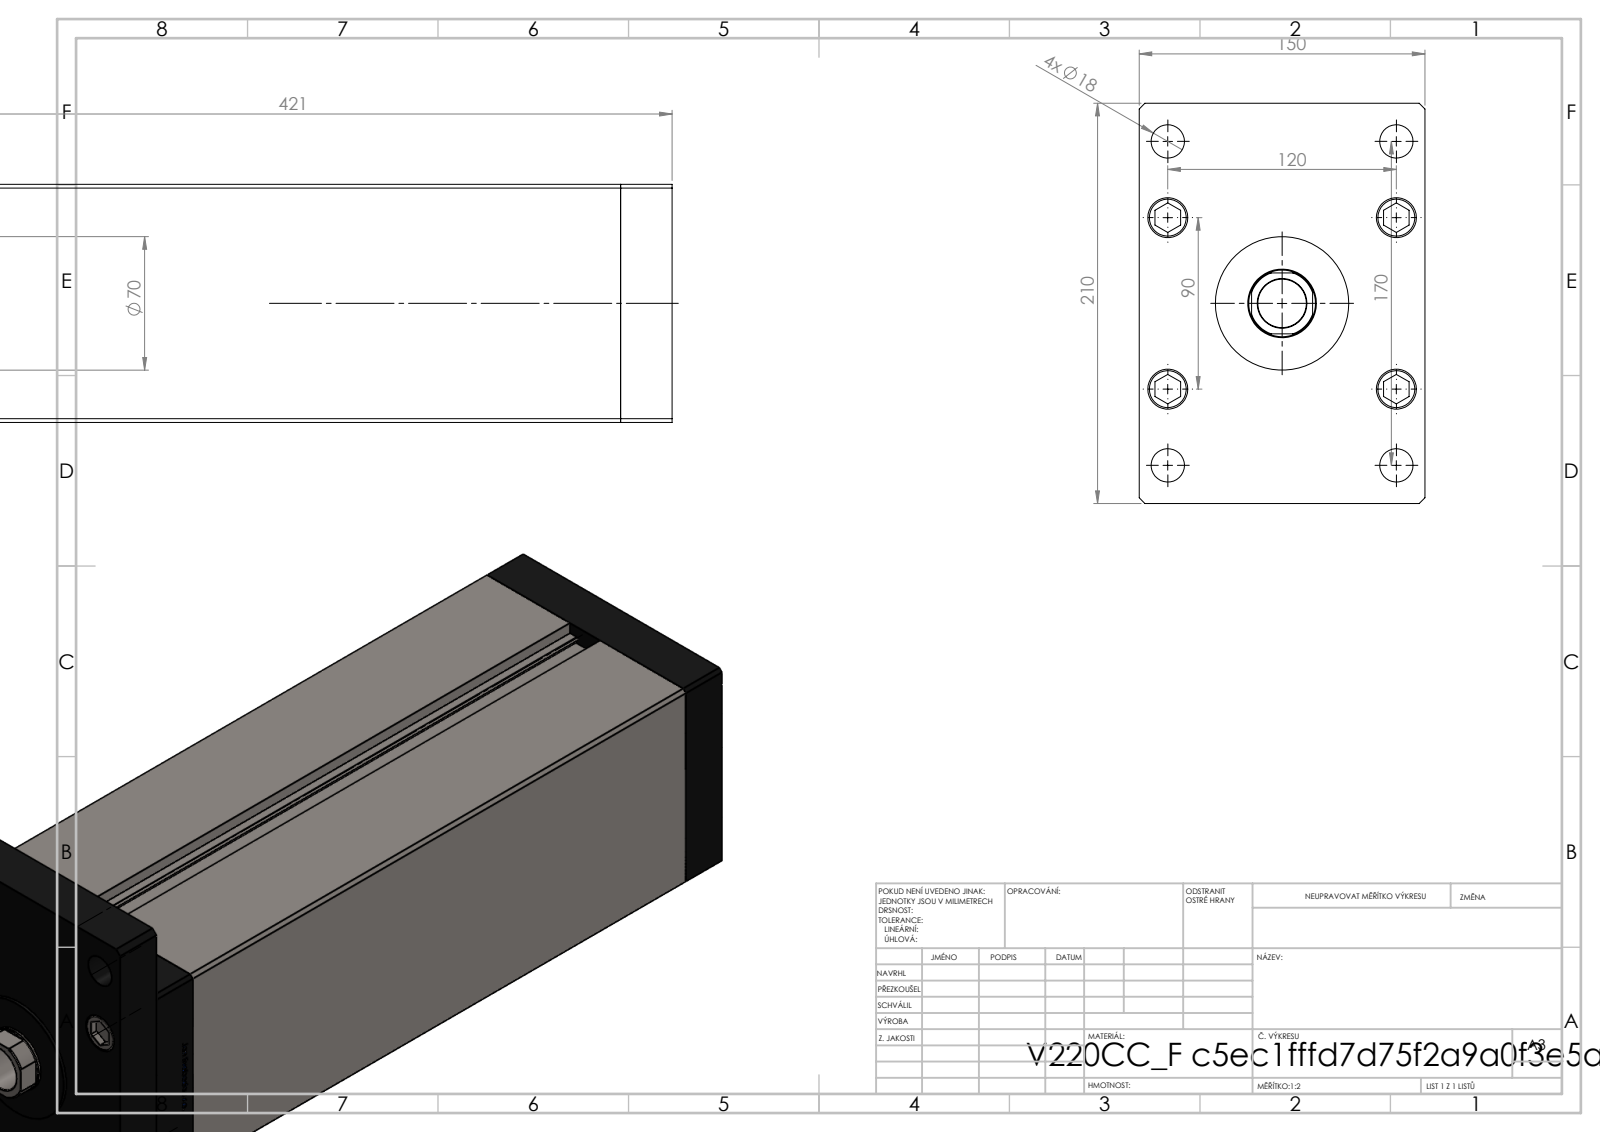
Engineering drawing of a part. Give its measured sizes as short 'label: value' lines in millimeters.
name: V220C_F; V220C BACK_F; V220C_VC_F; V220C_F_MIDDLE (+2 more)
written by: SolidWorks 2019 (CONFIG_CONTROL_DESIGN)
unit: mm
bodies: 19 solids, 1298 faces (513 planar, 179 cylindrical, 606 other)
size: 463 × 210 × 150
volume: 7 275 000 mm³; area: 657 603 mm²
holes: 9× ⌀17.5, 5× ⌀22, 4× ⌀16, 4× ⌀21, 1× ⌀25.5, 1× ⌀36, 1× ⌀37.5
bosses: 9× ⌀8, 5× ⌀21, 1× ⌀80, 1× ⌀70
rounds: 2× R0.93, 1× R17.5
face distances: 27, 150, 125, 394, 421, 367, 54, 448, 33.5, 6.5
hole spacings: 51, 40, 75, 104.04, 120, 126.49, 130, 176.92
